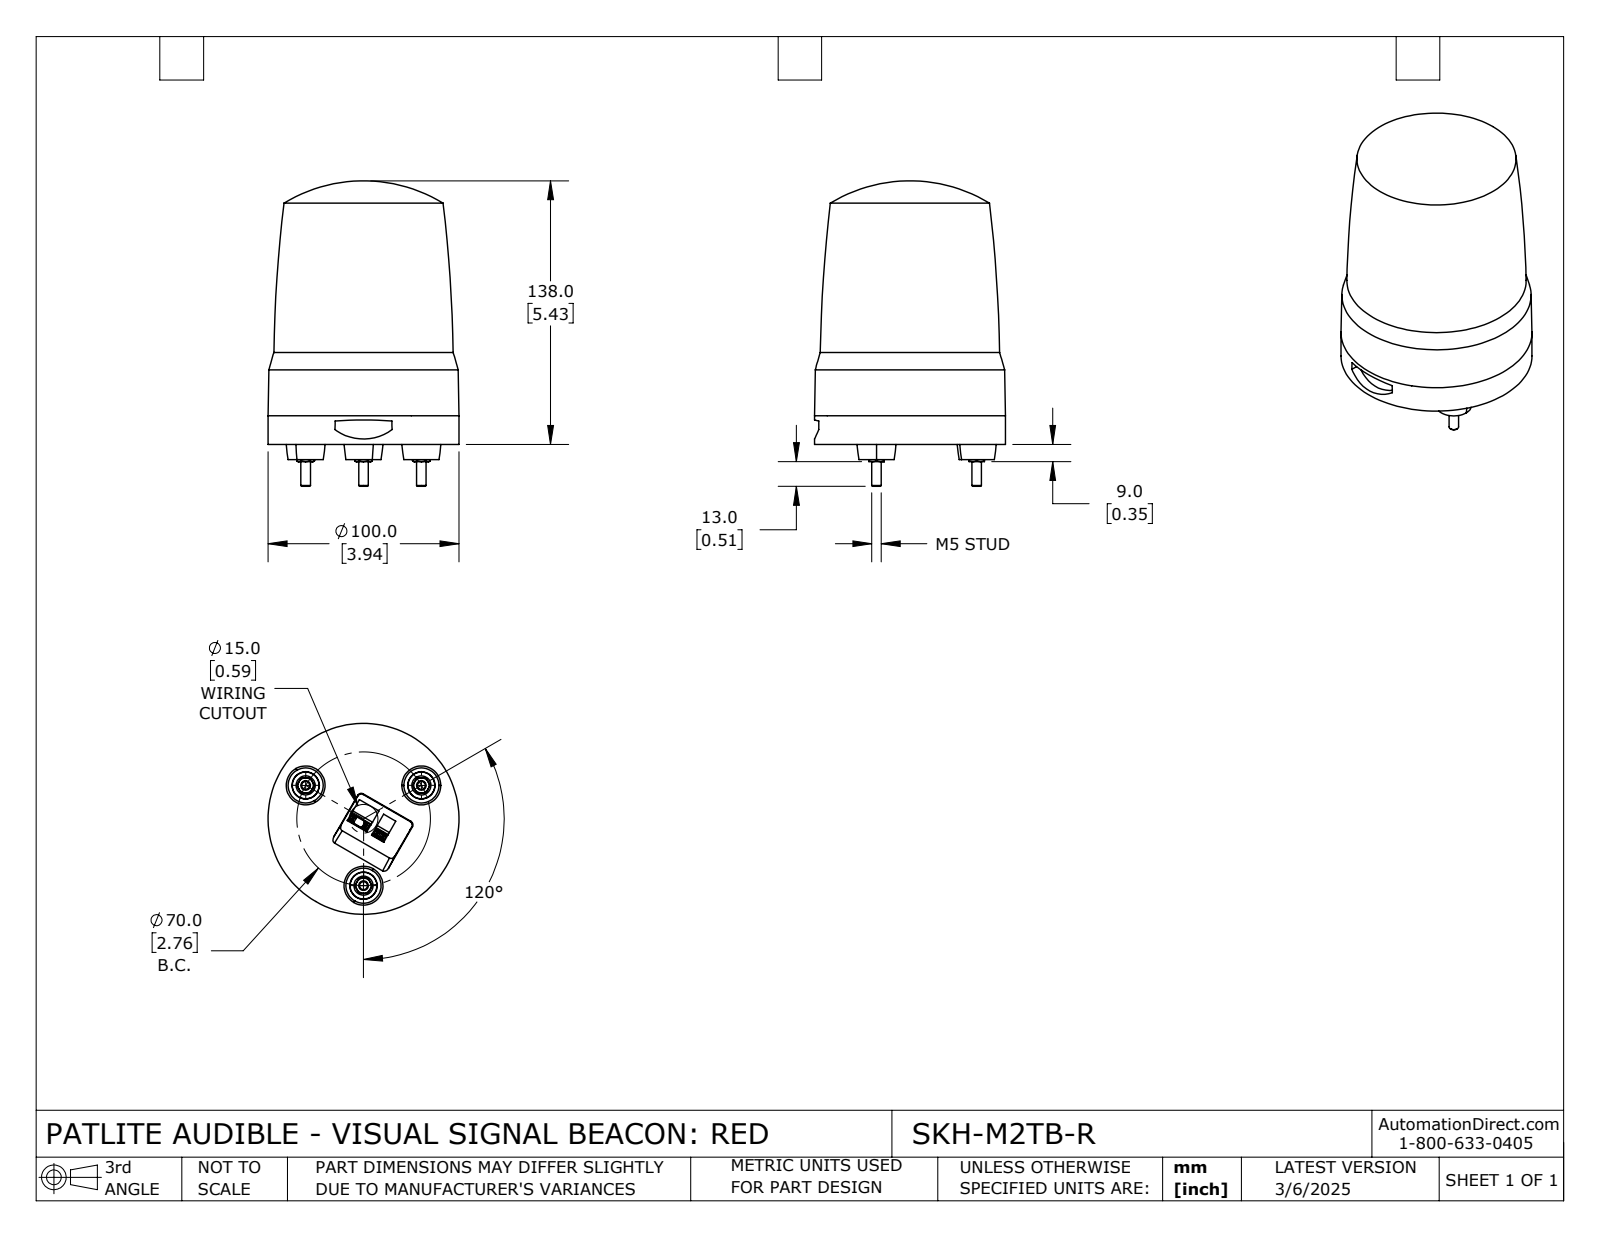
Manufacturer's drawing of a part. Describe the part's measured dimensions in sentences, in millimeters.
The part is named "SKH-M2TB-R". Its 3-D file was written by "SolidWorks 2024 (CONFIG_CONTROL_DESIGN)". It is 1 solid with 270 faces: 146 planar, 25 cylindrical and 99 other. Overall it measures 160 by 100 by 100 millimeters. Its volume is 895 705 cubic millimeters and its surface area 57 629 square millimeters. Round bosses or shafts: 3 of diameter 10, 3 of diameter 5, 1 of diameter 100. Partial cylindrical surfaces (rounded edges, fillets, slot ends): 4 of radius 2, 2 of radius 0.3, 2 of radius 5.05, 1 of radius 45, 1 of radius 80.12. The main face-to-face distances are 18.85, 8, 22, 26.85, 3, 3.8, 4.2, 23.05, 5.95, 14.82.
